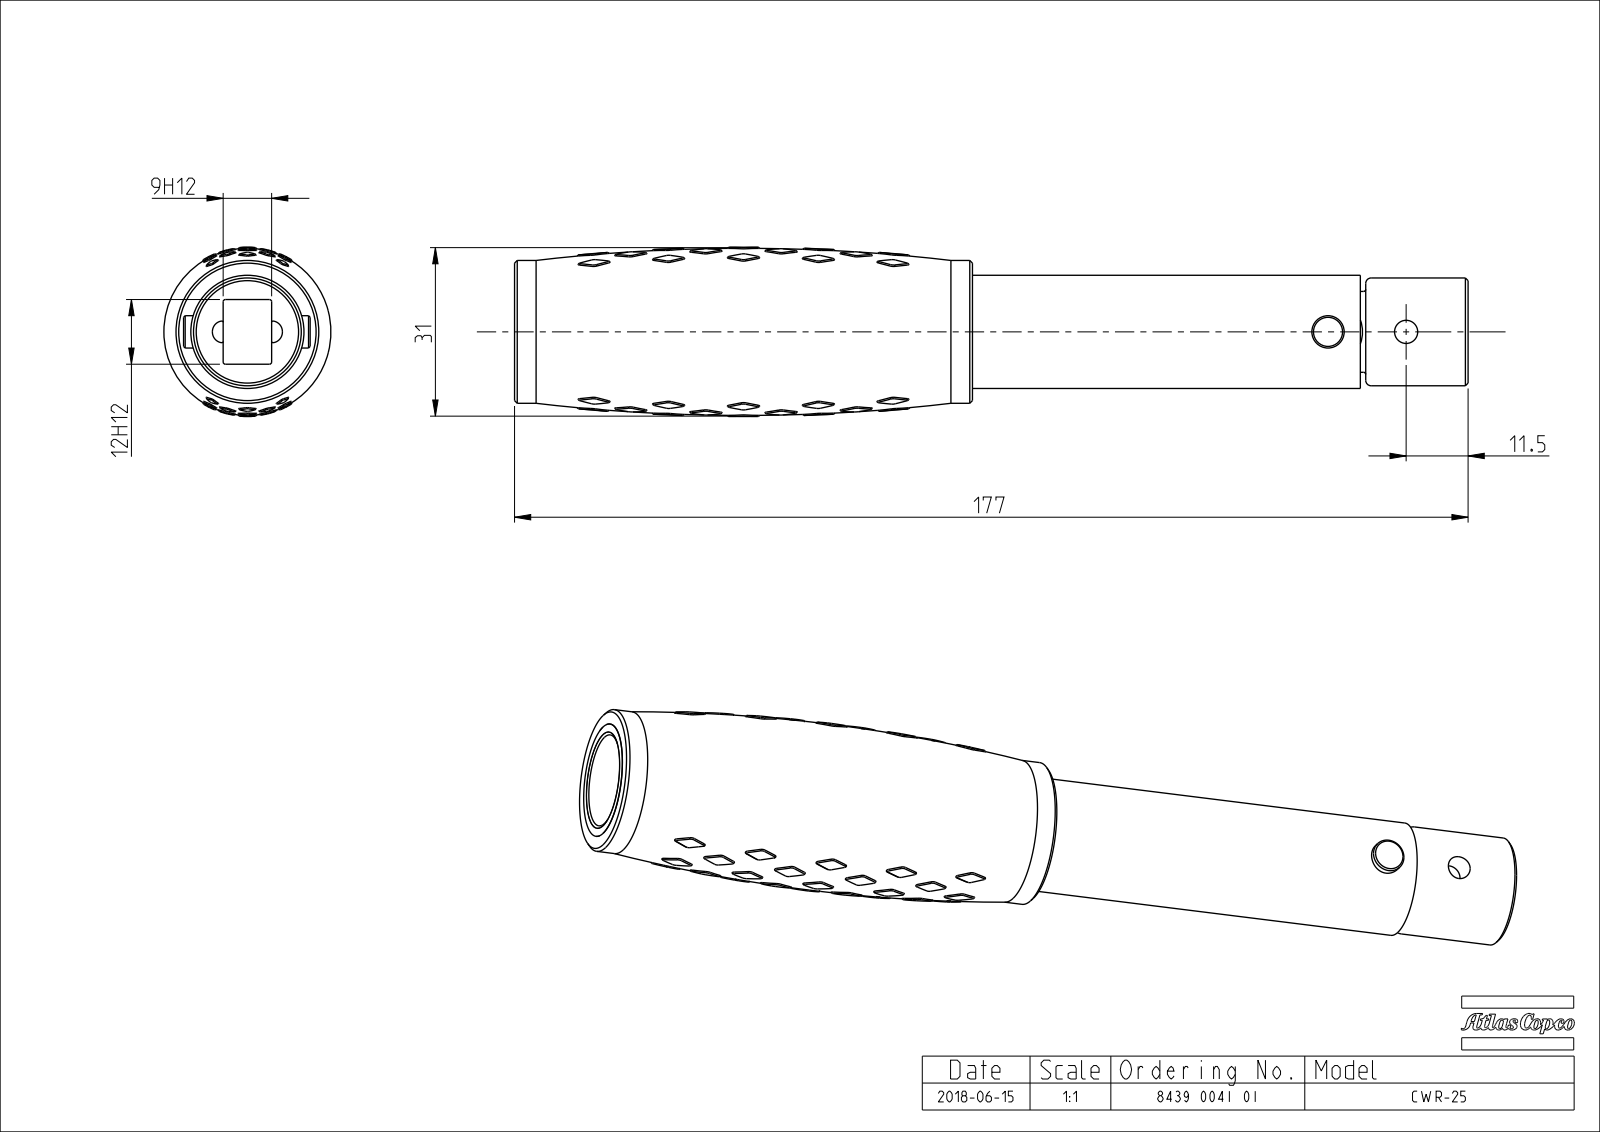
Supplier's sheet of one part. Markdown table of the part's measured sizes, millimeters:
| quantity | value |
| --- | --- |
| part name | 8439004101 |
| STEP written by | SolidWorks 2016 (AUTOMOTIVE_DESIGN) |
| units | millimeters |
| bodies | 0 solids, 474 faces (20 planar, 42 cylindrical, 412 other) |
| overall size | 177 × 31.41 × 31 |
| round holes (diameter × count) | 4.3 × 1, 16.5 × 1, 21 × 1, 26.5 × 1 |
| round bosses / shafts (diameter × count) | 20 × 1, 15 × 1, 12.8 × 1, 6 × 1 |
| partial cylindrical surfaces (radius × count) | 0.4 × 4, 2 × 4, 2.5 × 2, 8.5 × 1 |
| main face-to-face distances | 3, 82, 79, 85, 9, 12, 72, 75, 154, 157 |
